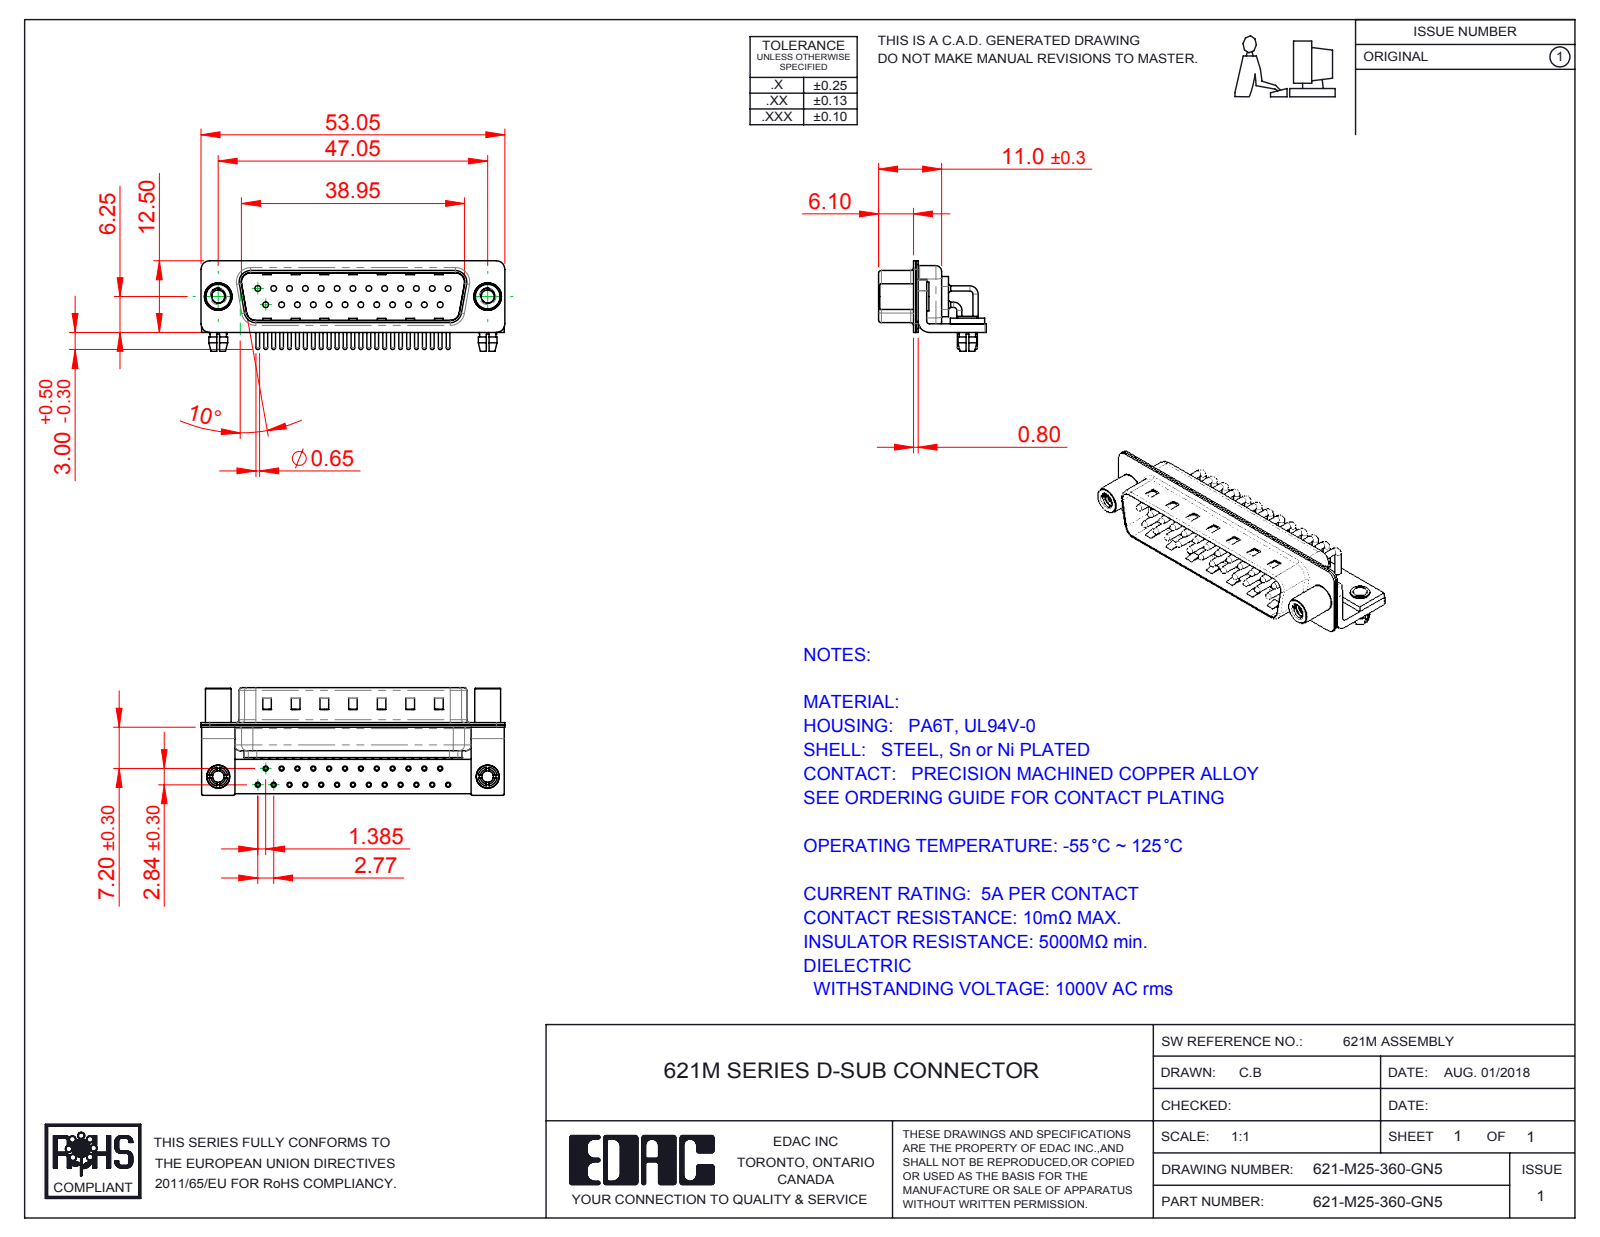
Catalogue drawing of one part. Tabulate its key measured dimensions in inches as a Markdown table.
| quantity | value |
| --- | --- |
| part name | 621-M25-360-GN5; 621M Contact Row 2; 621M Board Lock; 621M Contact Row 1 (+6 more) |
| STEP written by | SolidWorks 2016 (CONFIG_CONTROL_DESIGN) |
| units | inches |
| bodies | 35 solids, 3368 faces (1847 planar, 1183 cylindrical, 338 other) |
| overall size | 2.089 × 0.74 × 0.622 |
| volume | 0.217 in³ |
| surface area | 14.65 in² |
| round holes (diameter × count) | 0.079 × 27, 0.035 × 25, 0.039 × 25, 0.067 × 25, 0.089 × 2, 0.098 × 2, 0.126 × 2, 0.157 × 2, 0.189 × 2 |
| round bosses / shafts (diameter × count) | 0.035 × 33, 0.059 × 25, 0.026 × 25, 0.197 × 2, 0.193 × 2, 0.177 × 2, 0.157 × 2, 0.134 × 2 |
| partial cylindrical surfaces (radius × count) | 0.04 × 25, 0.01 × 16, 0.059 × 16, 0.079 × 13, 0.02 × 9, 0.063 × 8, 0.024 × 4, 0.026 × 4 |
| main face-to-face distances | 0.016, 0.033, 0.049, 0.059, 0.376, 0.031, 0.409, 0.327, 0.039, 0.075 |
| hole center spacings | 0.124, 0.109, 0.327, 0.218, 0.436, 0.545, 0.198, 0.654 |
